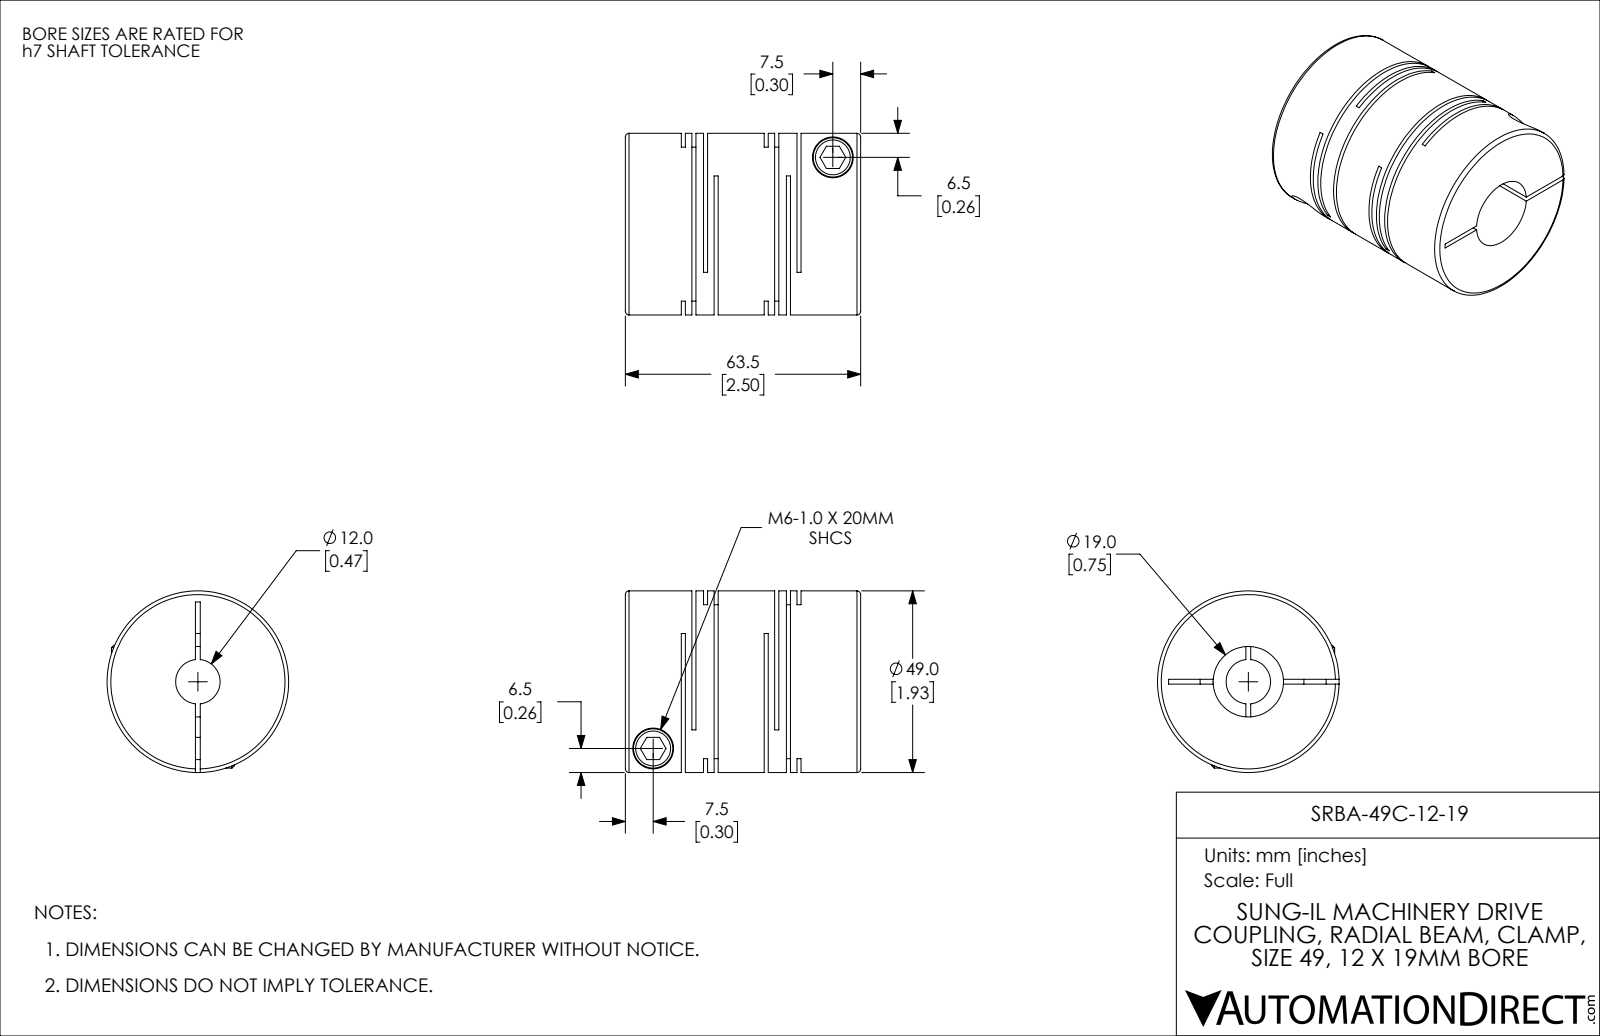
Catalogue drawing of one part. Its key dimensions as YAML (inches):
part_name: "SRBA-49C-12-19"
step_written_by: "SolidWorks 2021 (CONFIG_CONTROL_DESIGN)"
units: inches
bodies: {solids: 1, faces: 114, planar: 60, cylindrical: 42, other: 12}
overall_size: [2.5, 1.929, 1.929]
volume: 5.51
surface_area: 59.84
round_holes:
  - {diameter: 0.236, count: 2}
  - {diameter: 0.433, count: 2}
  - {diameter: 0.472, count: 1}
  - {diameter: 0.748, count: 1}
round_bosses_or_shafts:
  - {diameter: 0.417, count: 2}
  - {diameter: 1.929, count: 1}
face_to_face_distances: [0.236, 0.043, 0.88, 0.112, 0.069, 0.193, 0.837, 0.124, 0.768, 0.644]
